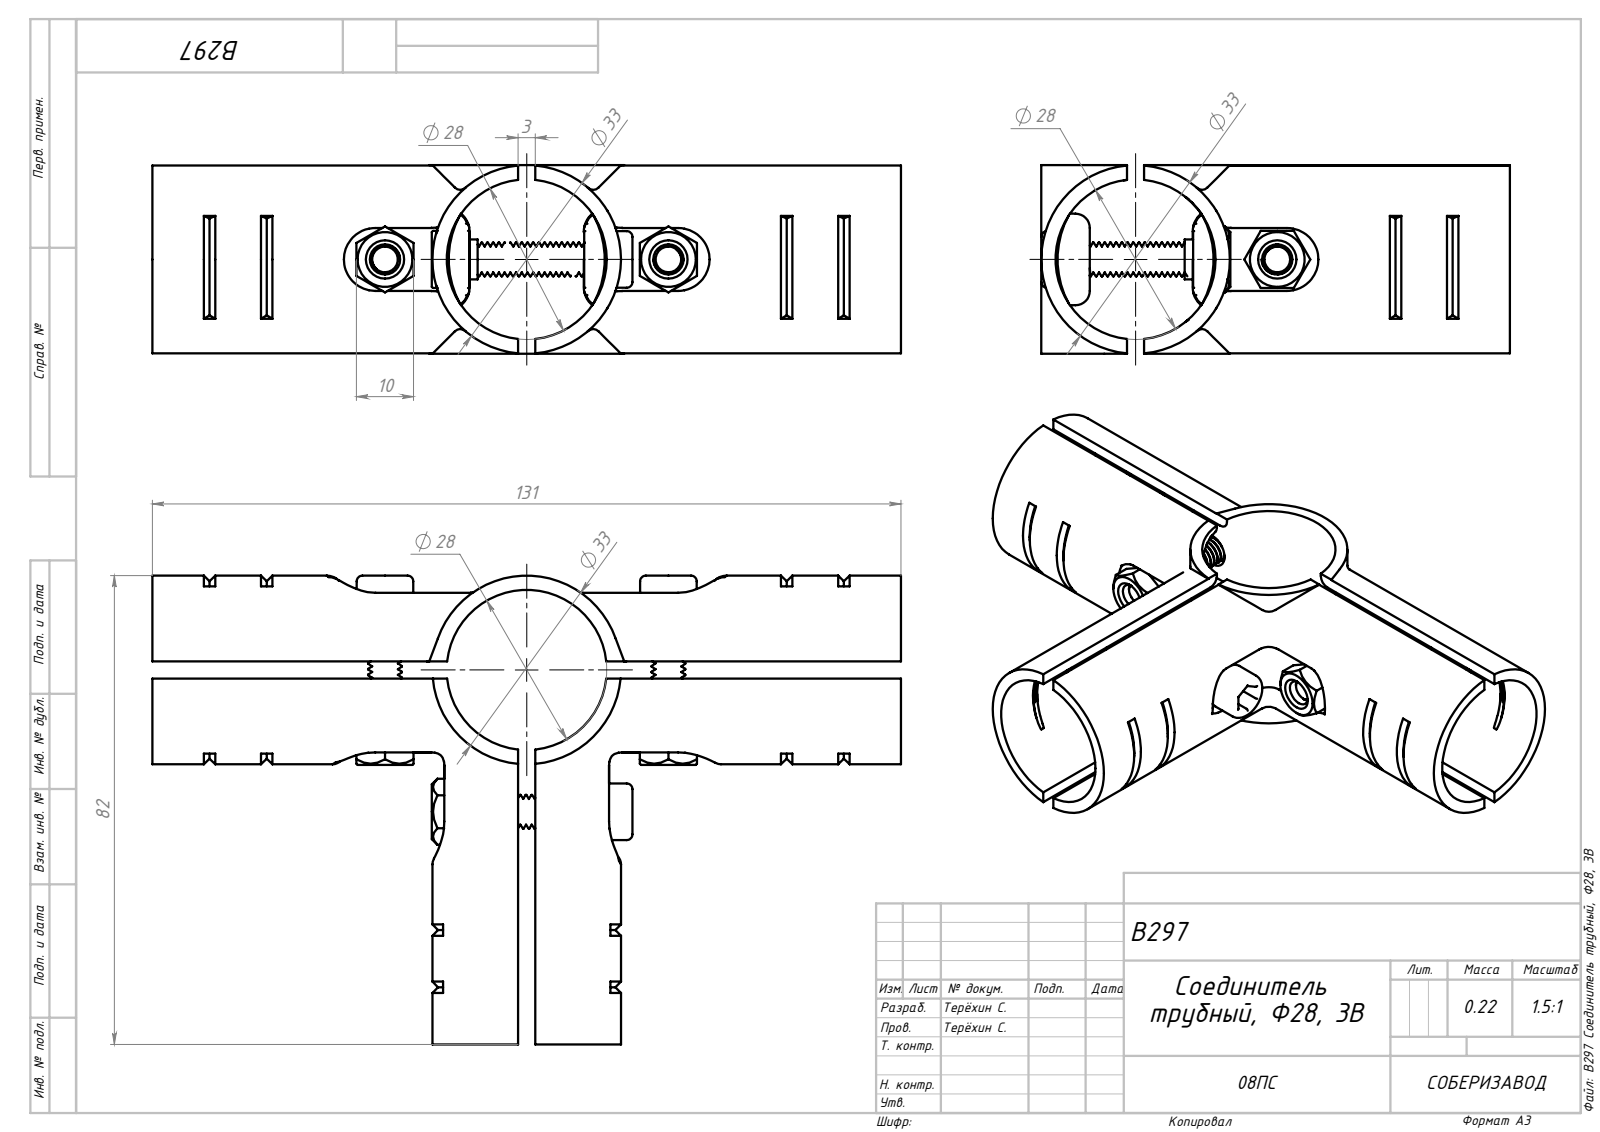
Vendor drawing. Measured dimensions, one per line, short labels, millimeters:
name: B297 Соединитель трубный, Ф28, 3B_00; B297 Соединитель трубный, Ф28, 3B
written by: SolidWorks 2022 (AUTOMOTIVE_DESIGN)
unit: mm
bodies: 9 solids, 641 faces (154 planar, 264 cylindrical, 223 other)
size: 131 × 82 × 33
volume: 42 282 mm³; area: 38 927 mm²
holes: 3× ⌀5.3, 3× ⌀7.3, 3× ⌀28
bosses: 3× ⌀33, 3× ⌀9.9, 3× ⌀7, 3× ⌀5.9
rounds: 16× R0.3, 6× R4, 4× R3, 4× R5, 4× R16.15, 3× R5.5, 2× R2.5, 2× R8
face distances: 3, 11, 14, 2.5, 64, 67, 53, 8.5, 20.5, 11.5
hole spacings: 24.8, 49.6
